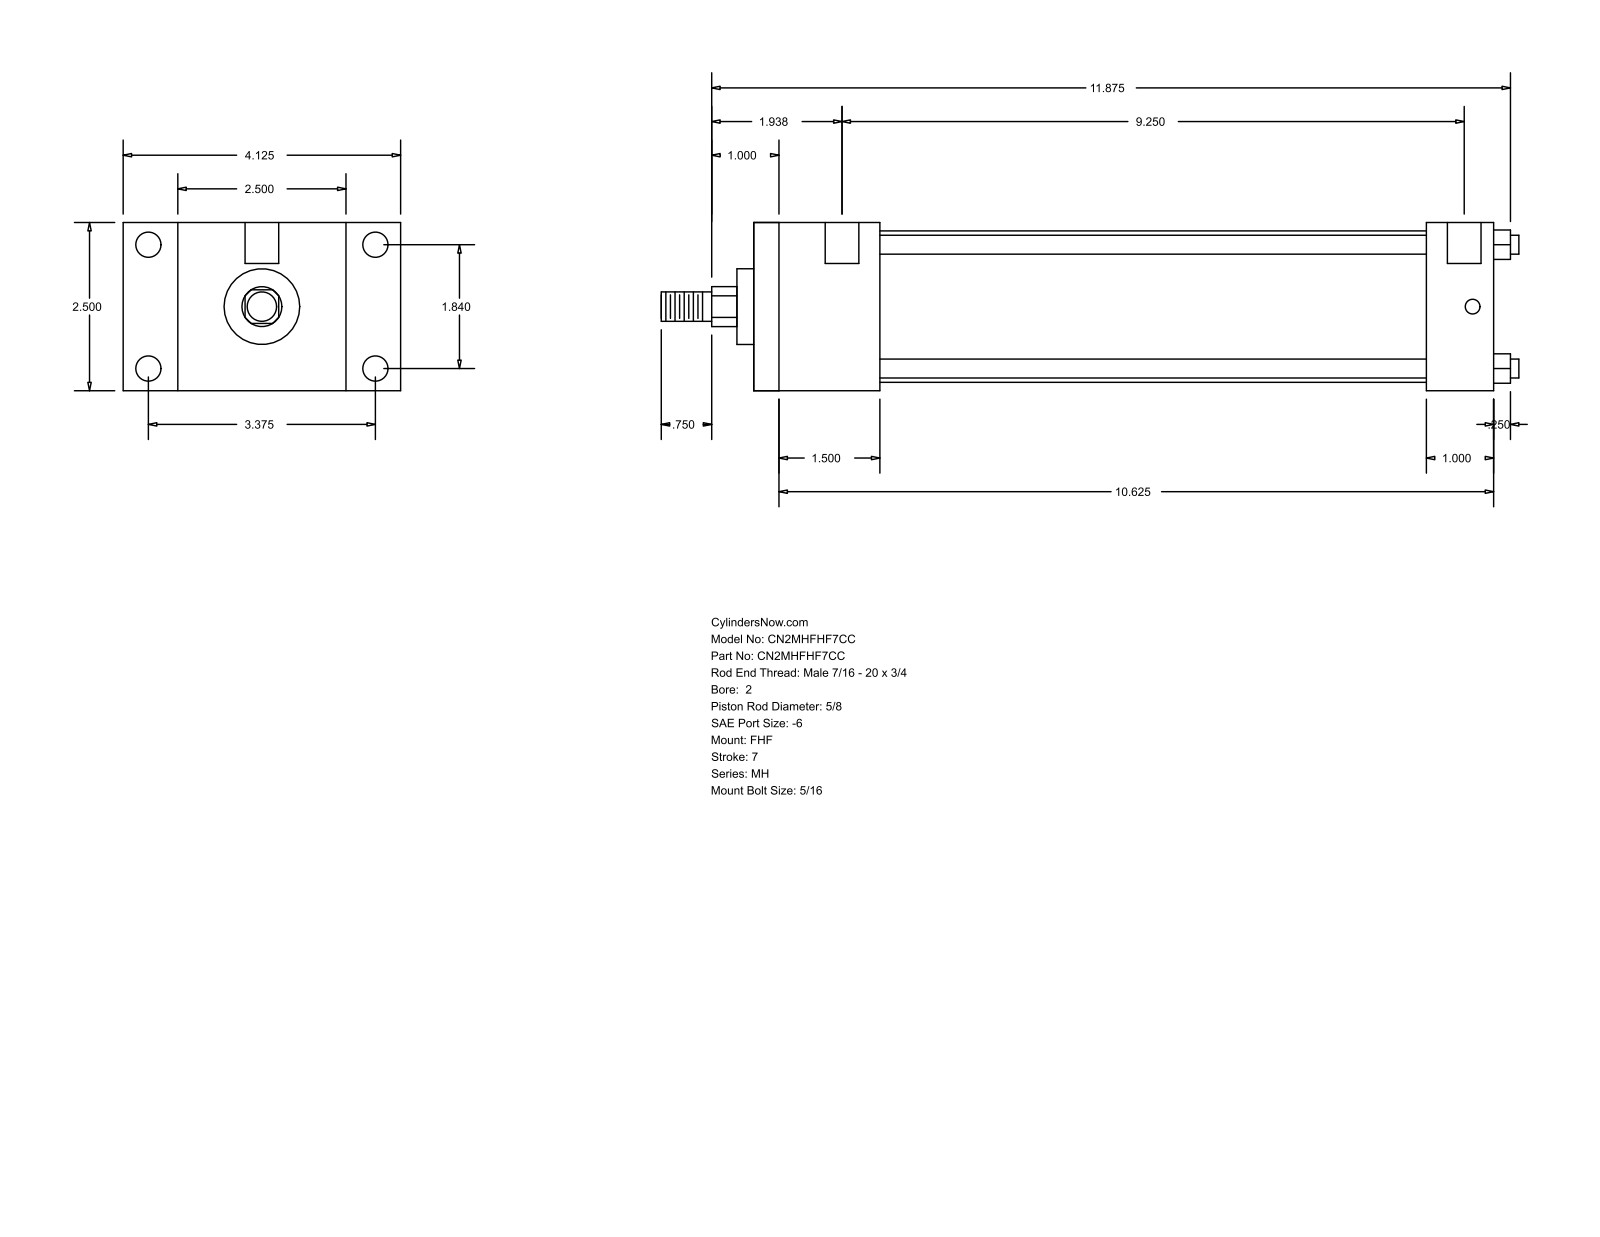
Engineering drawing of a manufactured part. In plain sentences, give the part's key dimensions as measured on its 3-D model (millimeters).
The part is named "MH_FHF__0200_0.625". Its 3-D file was written by "GSSL Pune (CONFIG_CONTROL_DESIGN)". It is 0 solids with 88 faces: 60 planar, 28 cylindrical and 0 other. Overall it measures 323.85 by 104.78 by 63.5 millimeters. Round holes: 4 of diameter 5.56, 4 of diameter 9.53, 2 of diameter 12.7. Round bosses or shafts: 4 of diameter 7.14, 1 of diameter 57.15, 1 of diameter 28.57, 1 of diameter 15.88, 1 of diameter 11.11. Partial cylindrical surfaces (rounded edges, fillets, slot ends): 1 of radius 7.54. The main face-to-face distances are 63.5, 47.62, 279.39, 231.77, 20.64, 84.14, 104.78, 254, 206.38, 25.39. The hole center spacings are 46.74, 85.72, 97.63, 242.89, 3.18, 4.76, 234.95, 238.13.
